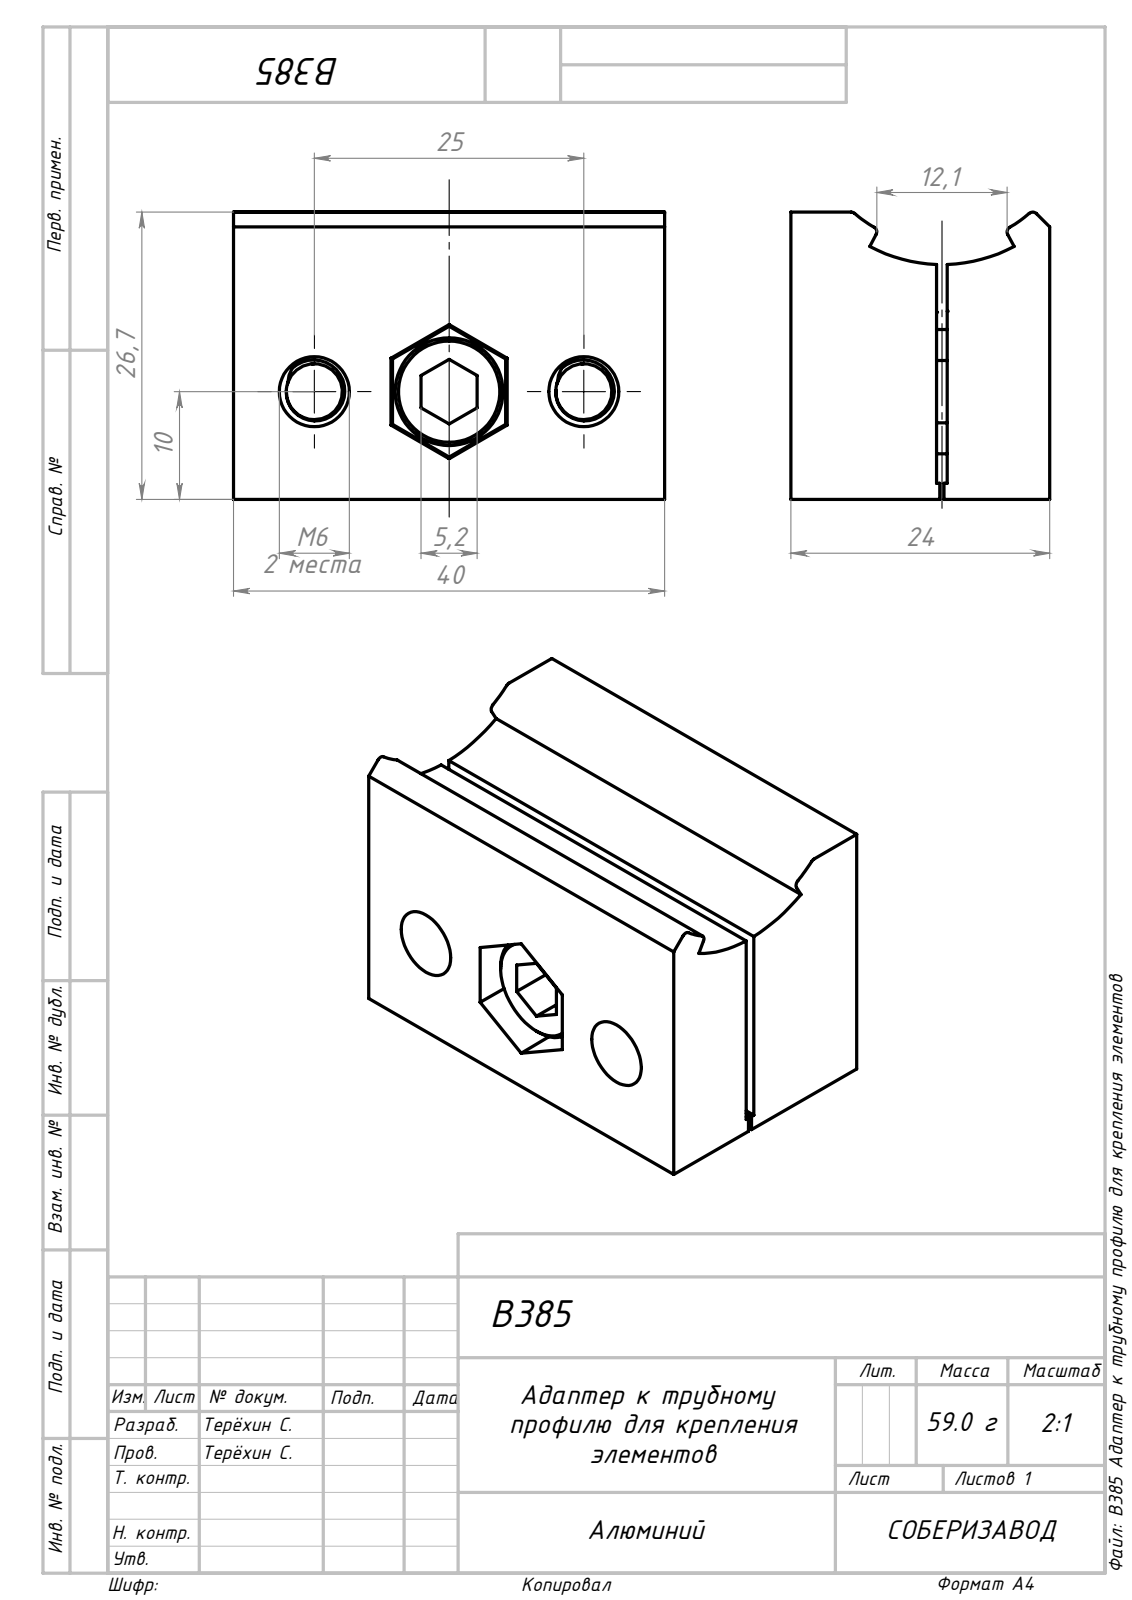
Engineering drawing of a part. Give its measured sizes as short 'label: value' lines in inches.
name: B385 Адаптер к трубному профилю для крепления элементов
written by: SolidWorks 2022 (AUTOMOTIVE_DESIGN)
unit: in
bodies: 6 solids, 301 faces (112 planar, 98 cylindrical, 91 other)
size: 1.575 × 1.05 × 0.945
volume: 1.14 in³; area: 18.27 in²
holes: 3× ⌀0.205, 3× ⌀0.256
bosses: 1× ⌀0.394, 1× ⌀0.374, 1× ⌀0.236
rounds: 12× R0.02, 4× R0.039, 2× R0.197, 1× R0.49, 1× R0.559
face distances: 0.945, 0.531, 0.374, 0.571, 0.492, 0.098, 0.413, 1.575, 0.039, 0.217
hole spacings: 0.492, 0.984
